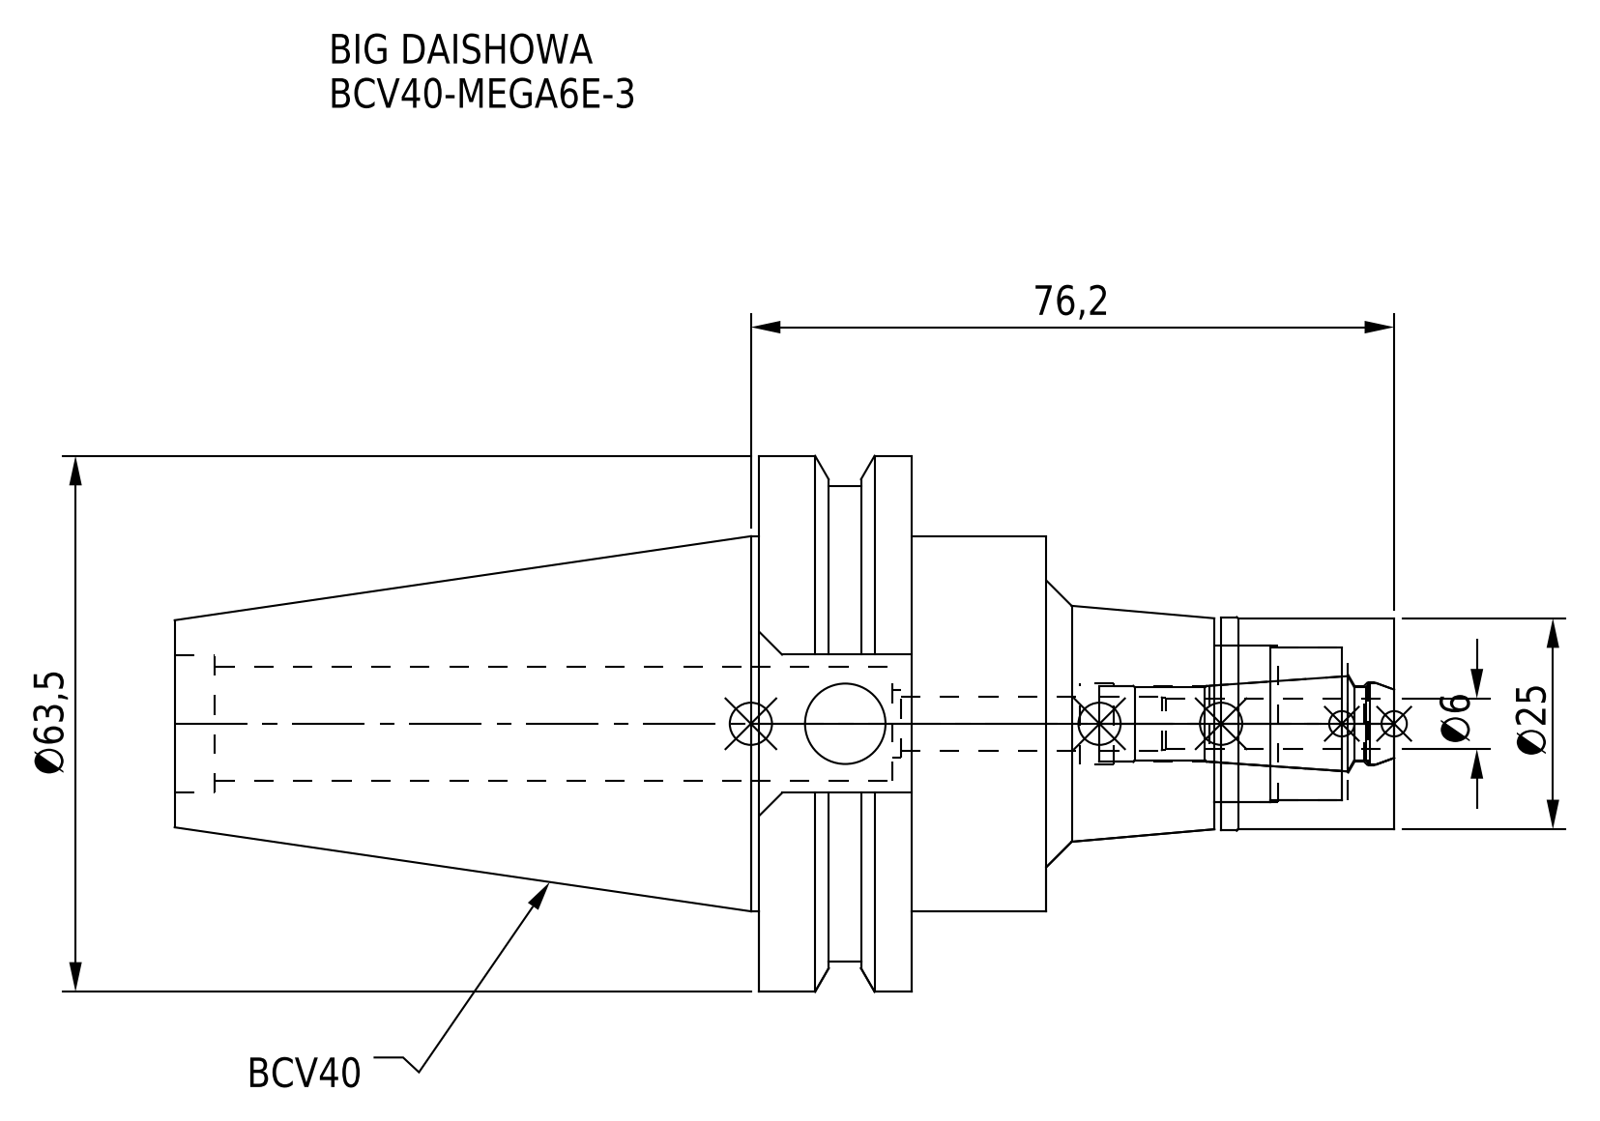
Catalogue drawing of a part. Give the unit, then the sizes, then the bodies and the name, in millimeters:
Units: millimetres
Overall size (bounding box): 144.45 × 63.5 × 61.35
Round holes (diameter × count): ⌀6.4 ×1, ⌀8 ×1, ⌀9 ×1, ⌀9.53 ×1, ⌀9.6 ×1, ⌀9.9 ×1, ⌀13.6 ×1, ⌀16.32 ×1, ⌀18 ×1, ⌀18.5 ×1
Round bosses / shafts (diameter × count): ⌀63.5 ×1, ⌀56.36 ×1, ⌀44.45 ×1, ⌀25.3 ×1, ⌀25 ×1
Main face-to-face distances: 18.05, 15.95, 34, 41.2, 57.15, 75.2, 144.45, 103.25, 87.3, 69.25
Volume: 147 208 mm³ · Surface area: 29 966 mm²
Bodies: 2 solids, 93 faces (31 planar, 42 cylindrical, 20 other)
Part name (STEP PRODUCT): MEN6_1.stp; BCV40-MEGA6E-3-060-FreeParts; BCV40-MEGA6E-3-060.stp; BCV40-MEGA6E-3 (+3 more)
STEP written by: SolidWorks 2019 (CONFIG_CONTROL_DESIGN)
